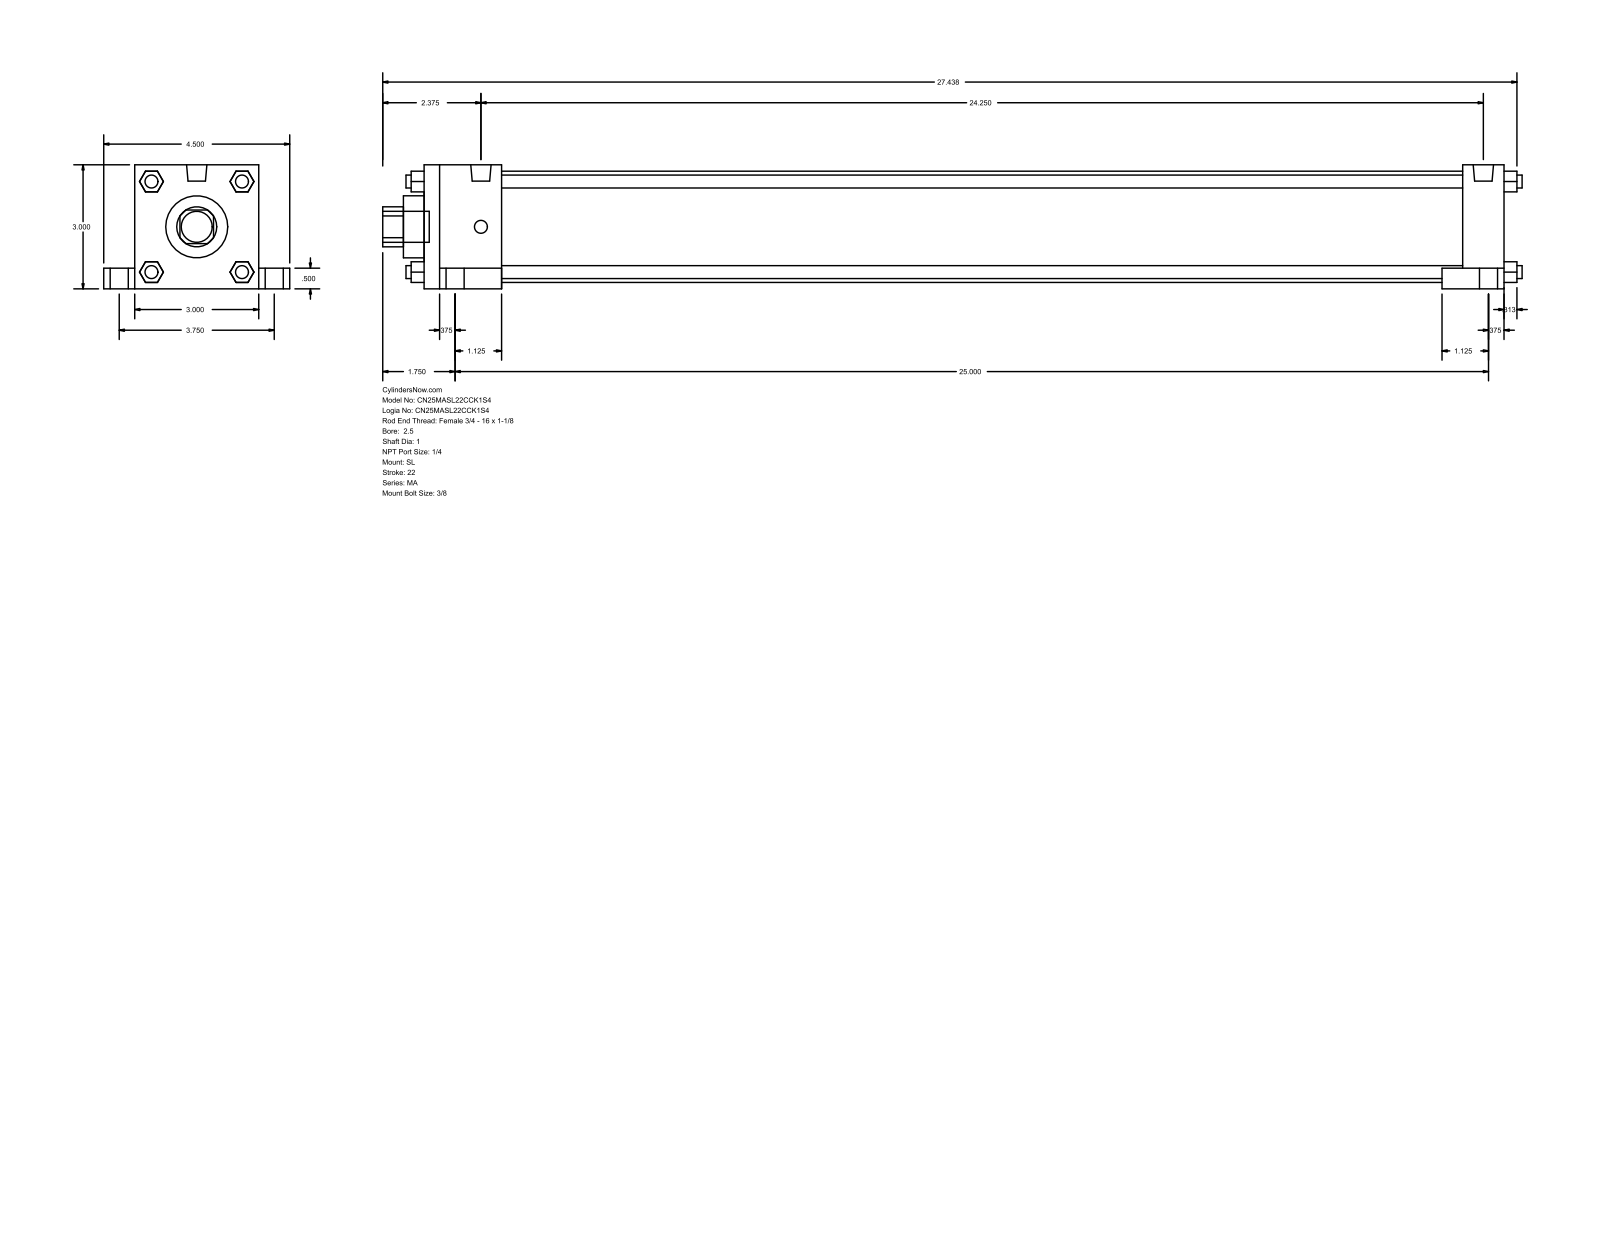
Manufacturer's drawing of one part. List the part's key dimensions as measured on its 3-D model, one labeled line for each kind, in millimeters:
Part name (STEP PRODUCT): MA_SL__0250_1
STEP written by: GSSL Pune (CONFIG_CONTROL_DESIGN)
Units: millimetres
Bodies: 0 solids, 148 faces (112 planar, 36 cylindrical, 0 other)
Overall size (bounding box): 700.09 × 114.3 × 76.2
Round holes (diameter × count): ⌀25.4 ×1, ⌀38.1 ×1, ⌀68.33 ×1
Round bosses / shafts (diameter × count): ⌀7.94 ×8, ⌀17.46 ×4, ⌀11.11 ×4, ⌀12.49 ×2, ⌀19.05 ×1
Partial cylindrical surfaces — rounded edges, fillets, slot ends (radius × count): R12.29 ×1
Main face-to-face distances: 76.2, 663.58, 12.7, 590.55, 25.4, 47.63, 615.95, 638.18, 19.05, 95.25
